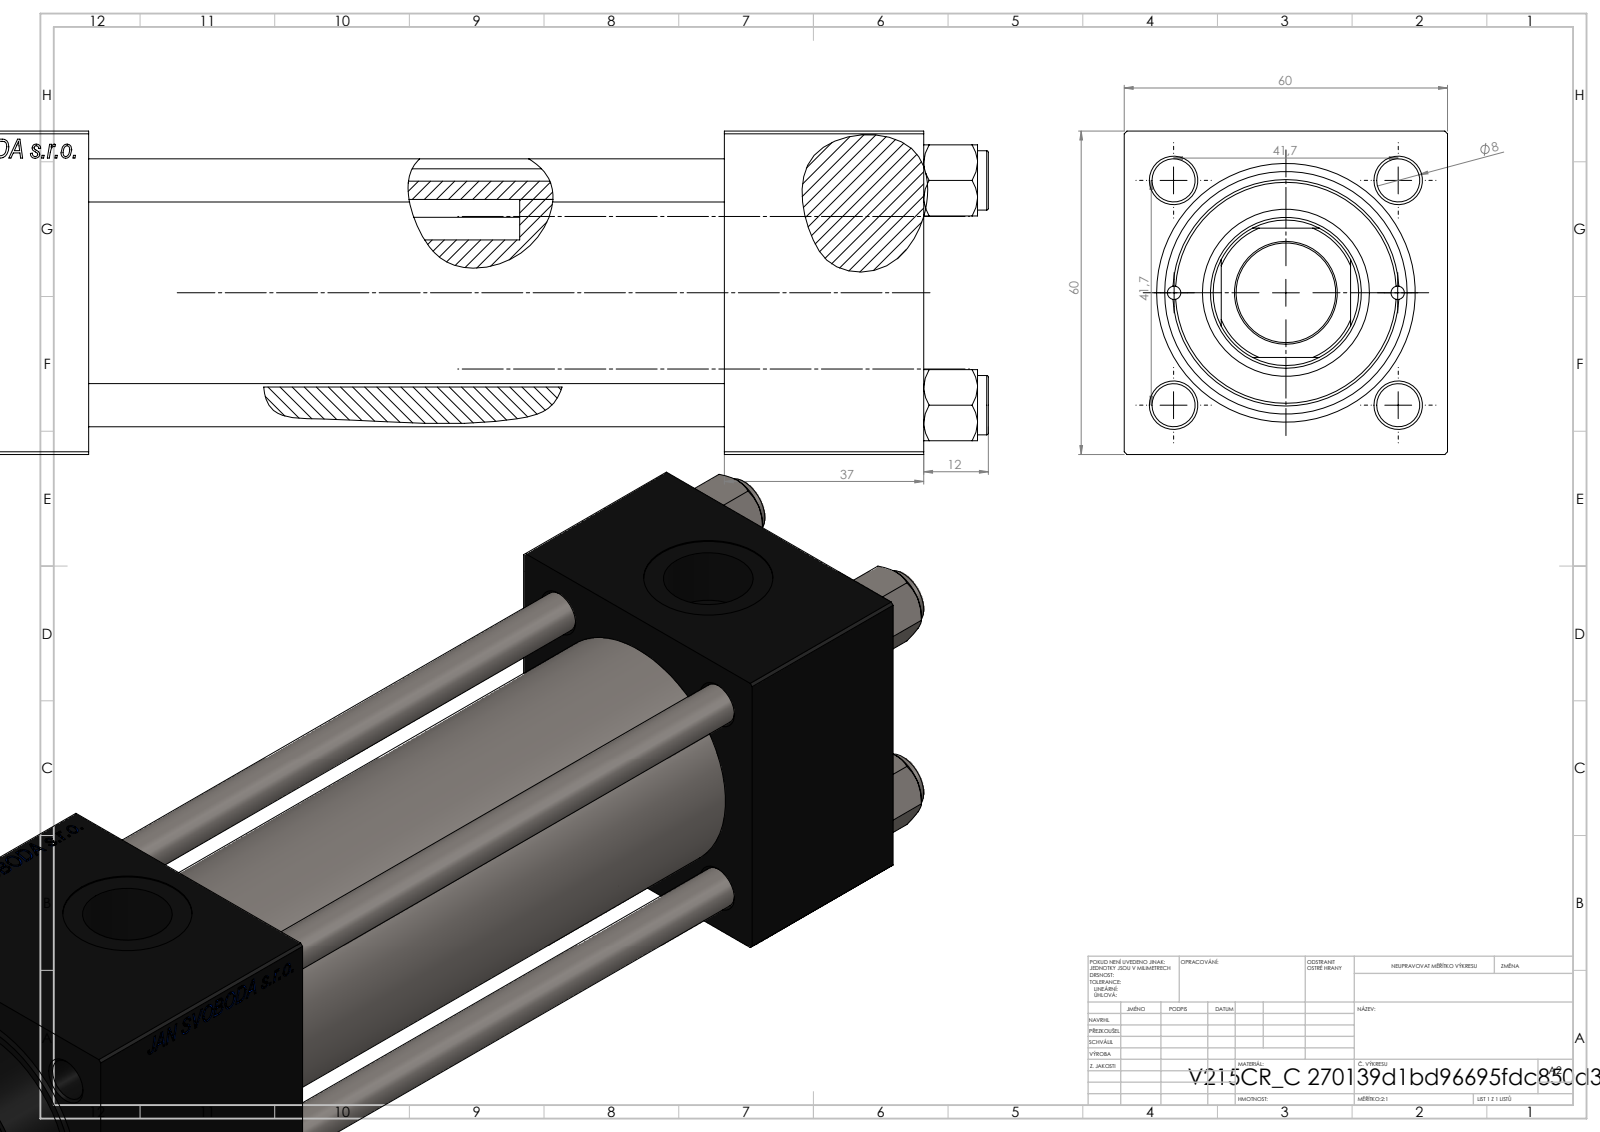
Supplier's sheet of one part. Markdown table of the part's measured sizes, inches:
| quantity | value |
| --- | --- |
| part name | NUT_M5_C; V215CR_VCP_C; V215_VC_A; V215CR_C_TYCINKA (+1 more) |
| STEP written by | SolidWorks 2019 (CONFIG_CONTROL_DESIGN) |
| units | inches |
| bodies | 11 solids, 1155 faces (528 planar, 91 cylindrical, 536 other) |
| overall size | 9.646 × 2.362 × 2.362 |
| volume | 30.35 in³ |
| surface area | 215.6 in² |
| round holes (diameter × count) | 0.315 × 4, 0.098 × 2, 0.276 × 2, 0.656 × 2, 0.945 × 2, 0.728 × 1, 1.102 × 1, 1.22 × 1, 1.575 × 1, 1.772 × 1 |
| round bosses / shafts (diameter × count) | 0.433 × 4, 1.811 × 1, 1.654 × 1 |
| partial cylindrical surfaces (radius × count) | 0.531 × 1 |
| main face-to-face distances | 2.362, 1.457, 6.102, 4.646, 7.059, 5.602, 0.957, 2.087, 8.189, 6.732 |
| hole center spacings | 0.821, 1.161, 1.642, 1.832, 0.817, 2.322, 1.634, 6.004 |
